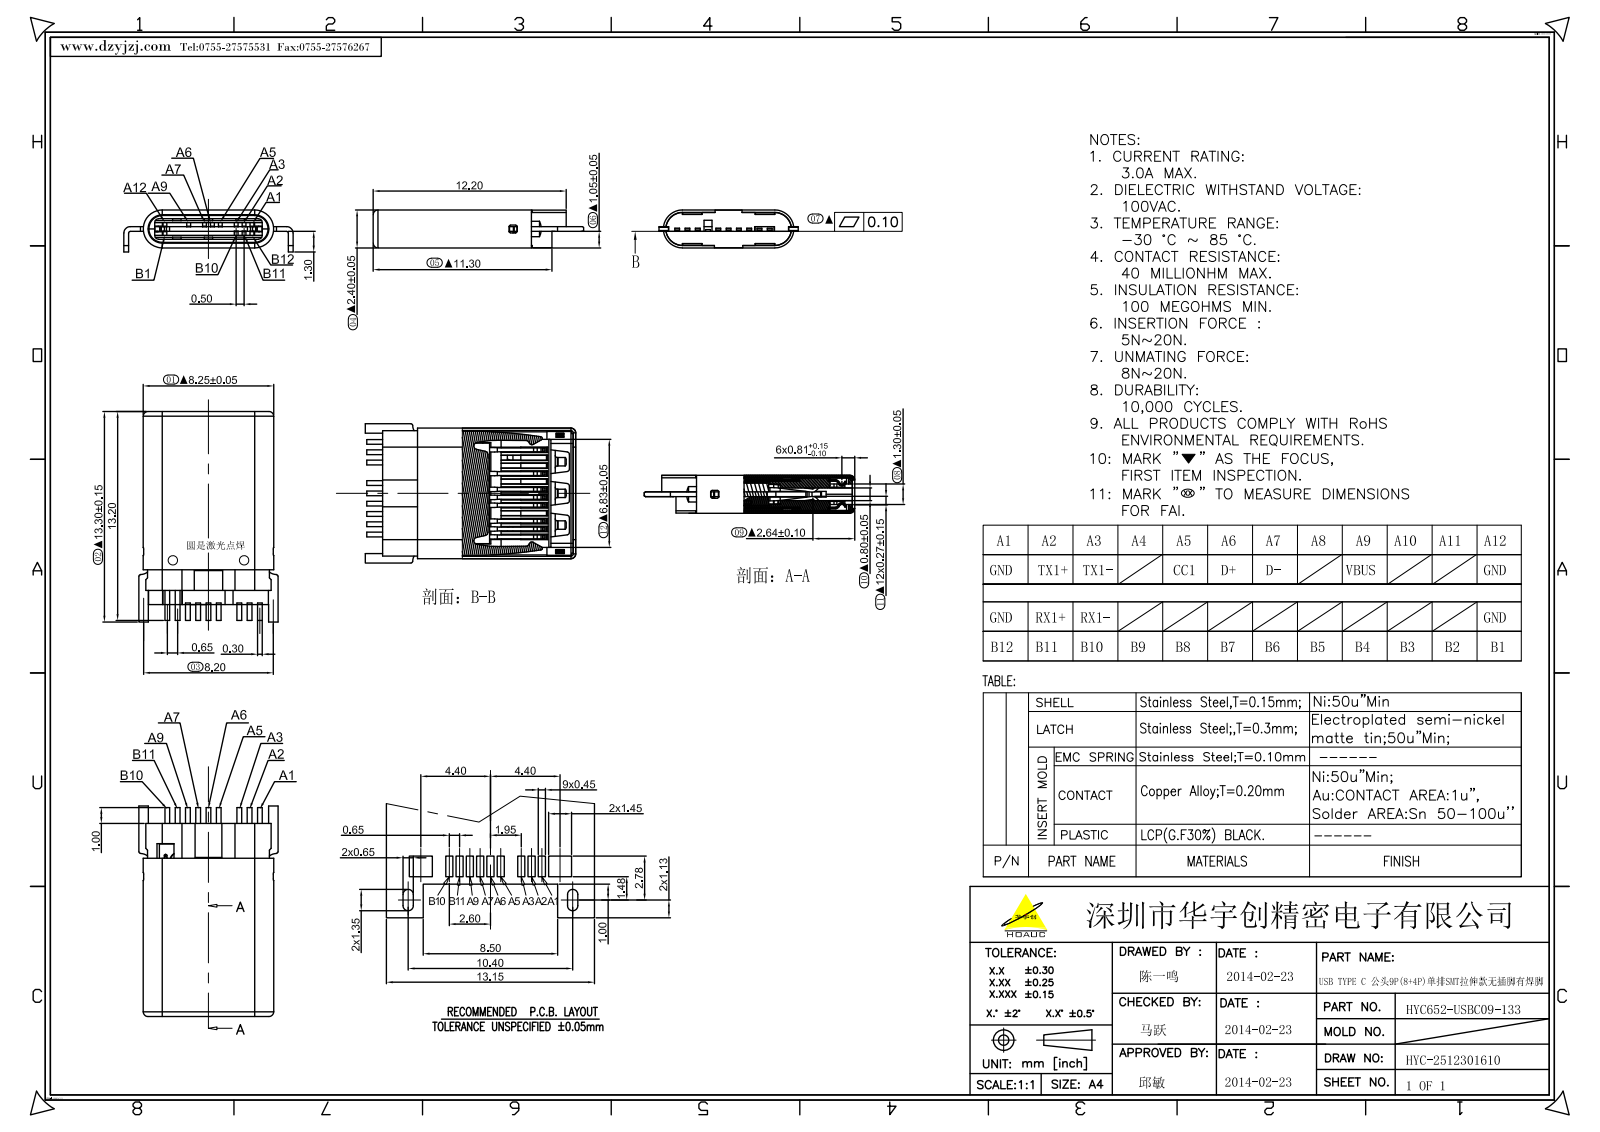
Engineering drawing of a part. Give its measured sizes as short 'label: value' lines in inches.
name: TANPIAN-PLASTIC_1_2__2_1_1_2_12
written by: CREO PARAMETRIC BY PTC INC, 2022073 (CONFIG_CONTROL_DESIGN)
unit: in
bodies: 1 solid, 391 faces (299 planar, 88 cylindrical, 4 other)
size: 0.524 × 0.346 × 0.094
volume: 0.011 in³; area: 0.631 in²
holes: 2× ⌀0.024
rounds: 10× R0.004, 10× R0.006, 6× R0.01, 6× R0.012, 6× R0.041, 2× R0.023, 2× R0.024, 2× R0.028
face distances: 0.031, 0.094, 0.063, 0.041, 0.022, 0.02, 0.053, 0.073, 0.051, 0.02
hole spacings: 0.176
